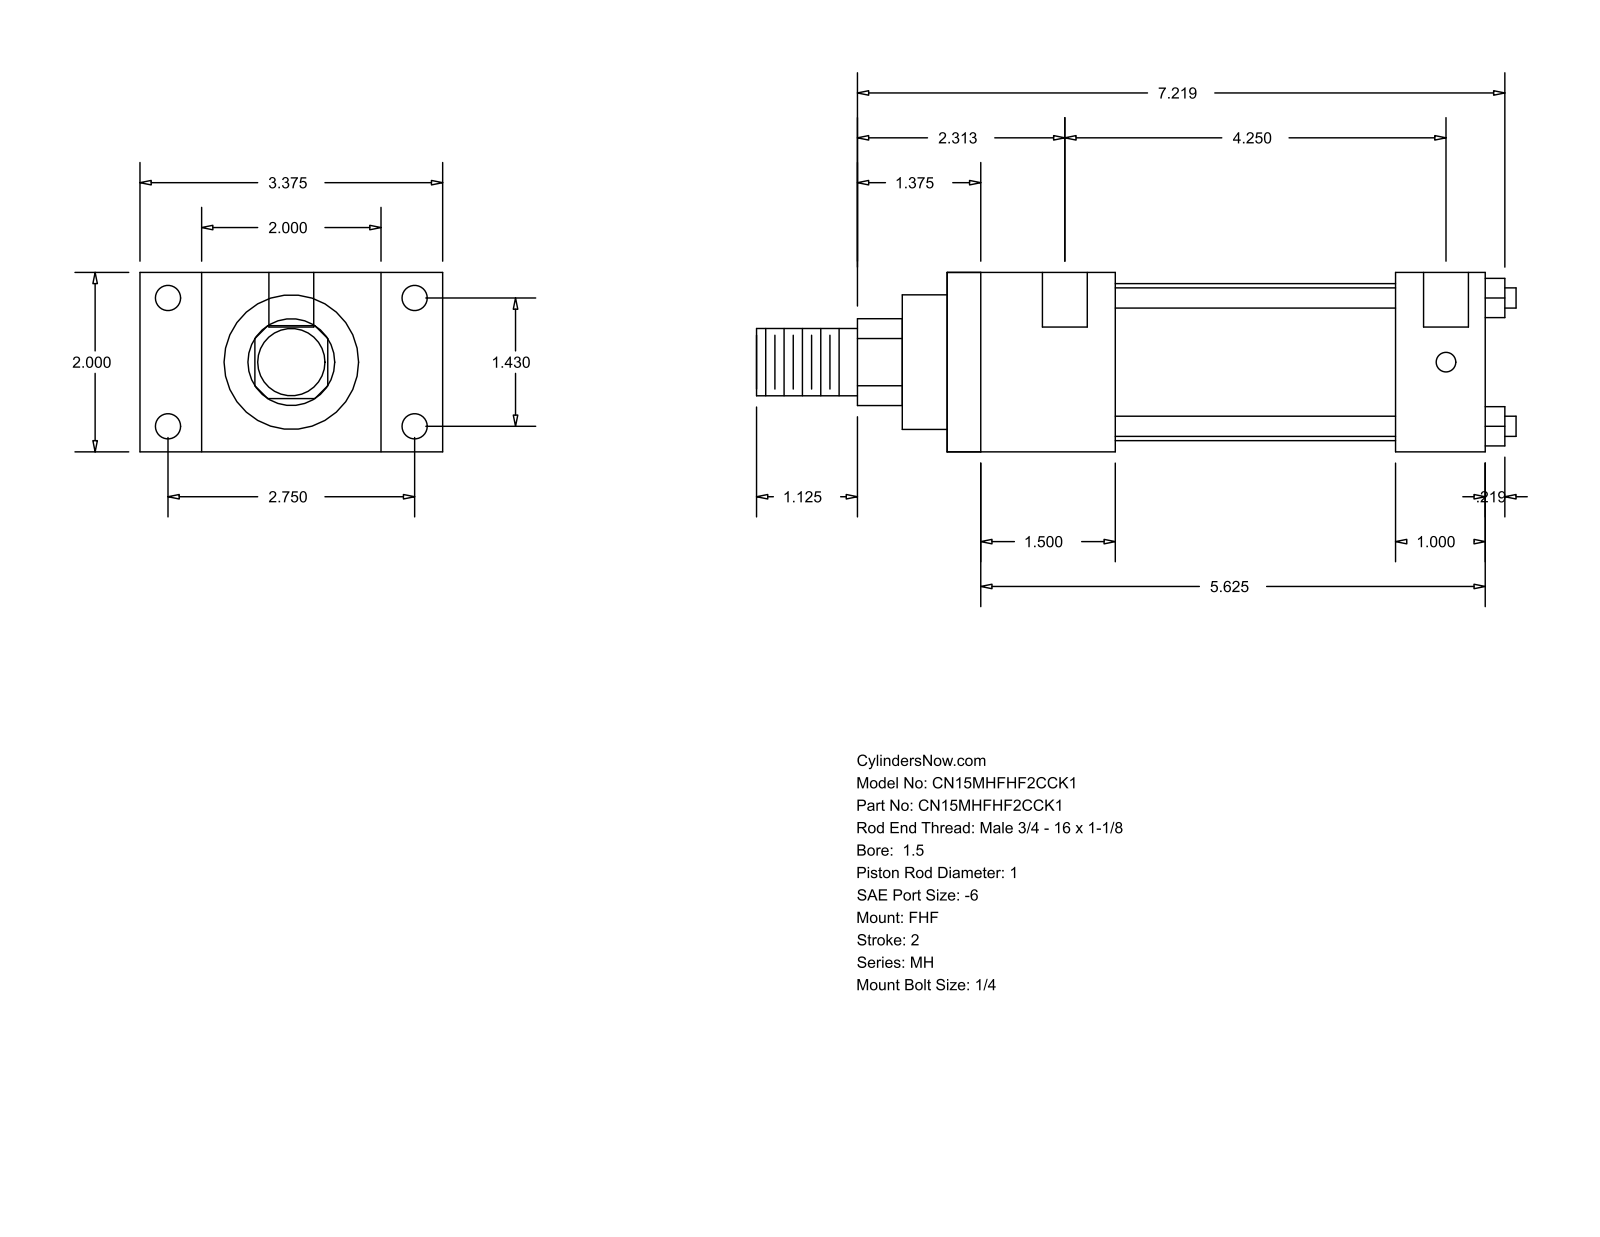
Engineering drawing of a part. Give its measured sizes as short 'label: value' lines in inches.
name: MH_FHF__0150_1
written by: GSSL Pune (CONFIG_CONTROL_DESIGN)
unit: in
bodies: 0 solids, 88 faces (60 planar, 28 cylindrical, 0 other)
size: 8.469 × 3.375 × 2
holes: 4× ⌀0.219, 4× ⌀0.281, 2× ⌀0.5
bosses: 4× ⌀0.225, 1× ⌀1.75, 1× ⌀1.5, 1× ⌀1, 1× ⌀0.75
rounds: 1× R0.484
face distances: 2, 0.687, 2.687, 1.875, 3.375, 6, 4.125, 1, 5, 3.125
hole spacings: 1.43, 2.75, 3.099, 4.375, 0.125, 4.25
